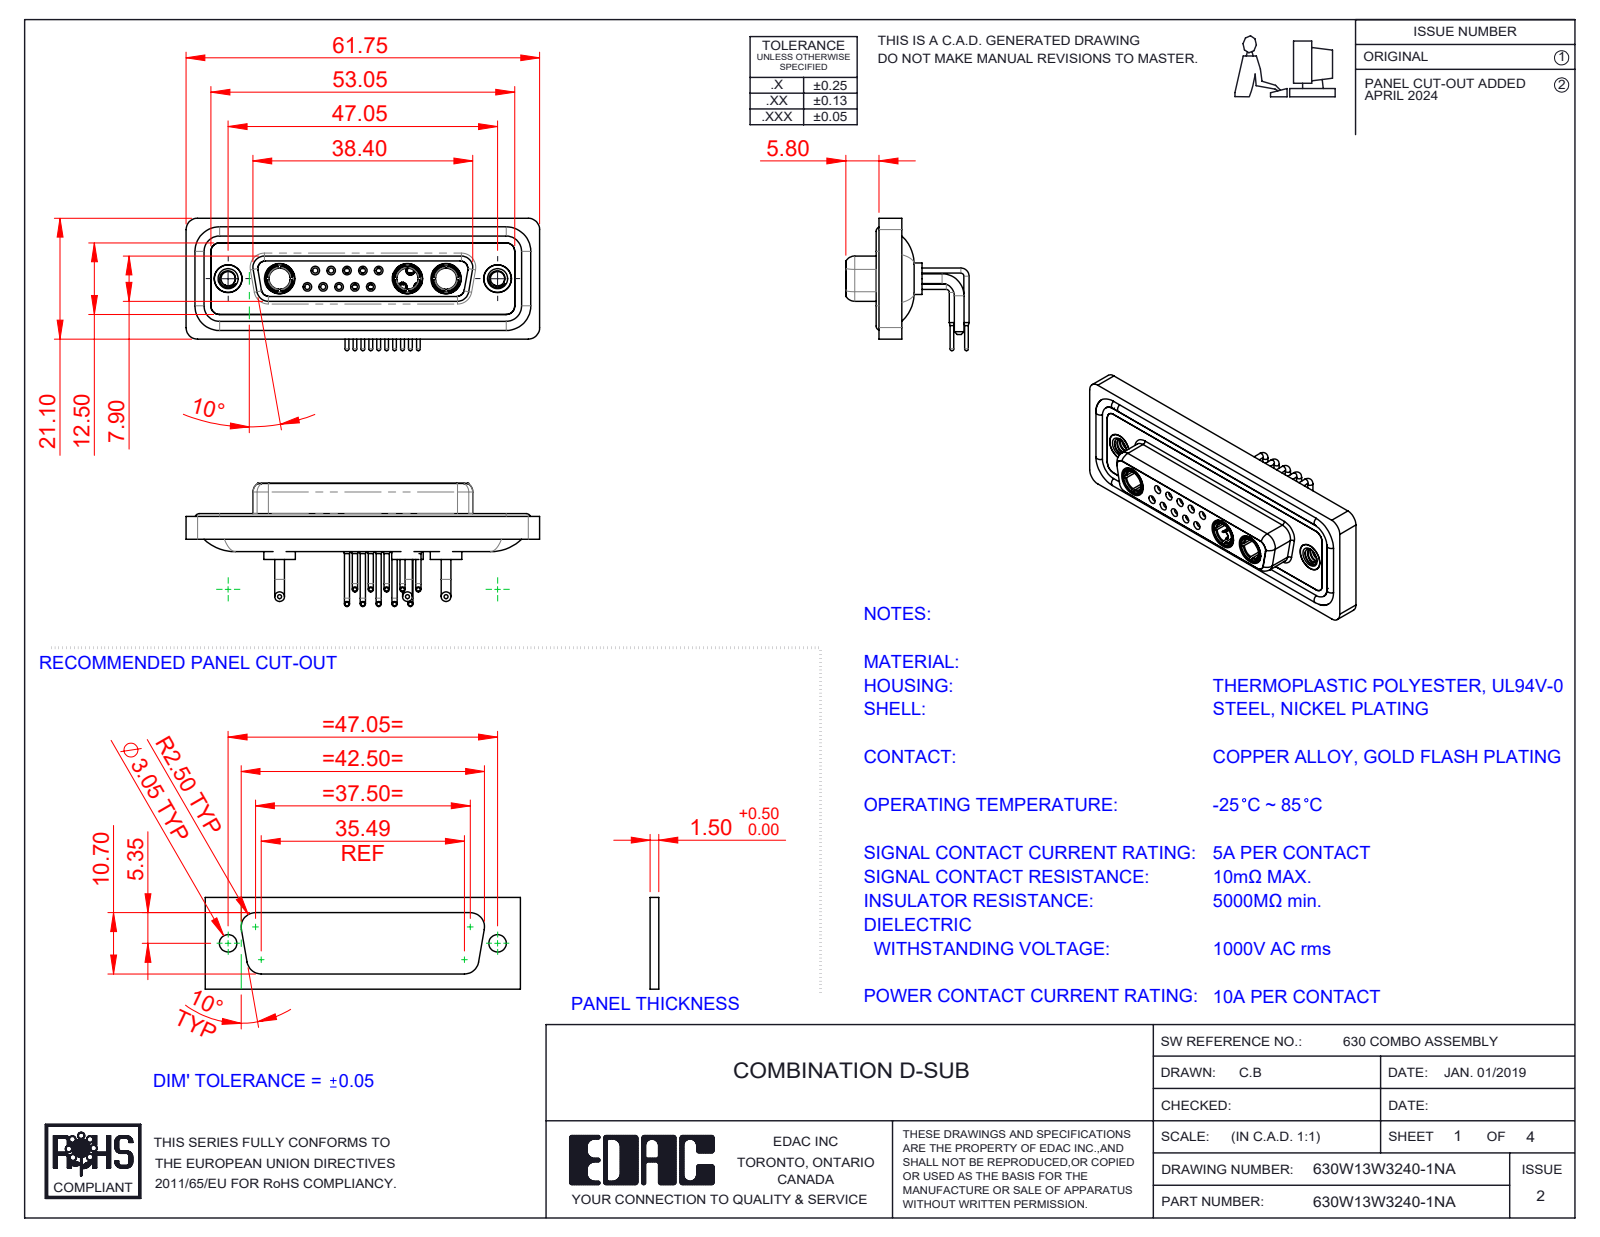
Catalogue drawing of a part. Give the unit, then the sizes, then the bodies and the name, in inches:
Units: inches
Overall size (bounding box): 2.431 × 0.91 × 0.848
Round holes (diameter × count): ⌀0.035 ×10, ⌀0.043 ×10, ⌀0.059 ×10, ⌀0.079 ×10, ⌀0.063 ×5, ⌀0.067 ×5, ⌀0.191 ×5, ⌀0.146 ×3, ⌀0.209 ×3, ⌀0.098 ×2, ⌀0.157 ×2, ⌀0.159 ×2
Round bosses / shafts (diameter × count): ⌀0.035 ×15, ⌀0.063 ×12, ⌀0.026 ×10, ⌀0.067 ×6, ⌀0.079 ×5, ⌀0.059 ×5, ⌀0.217 ×3, ⌀0.205 ×3
Partial cylindrical surfaces — rounded edges, fillets, slot ends (radius × count): R0.059 ×18, R0.079 ×18, R0.053 ×8, R0.063 ×8, R0.01 ×4, R0.02 ×4, R0.024 ×4, R0.026 ×4
Main face-to-face distances: 0.016, 0.071, 0.161, 0.043, 0.063, 0.059, 0.122, 0.098, 0.146, 0.055
Hole centre spacings: 0.124, 0.109, 0.218, 0.198, 0.327, 0.198, 0.295, 0.436
Volume: 0.506 in³ · Surface area: 21.93 in²
Bodies: 23 solids, 1144 faces (342 planar, 491 cylindrical, 311 other)
Part name (STEP PRODUCT): 630Combo Shell Rear_25 Contacts; 630W13W3240-1NA; 630Combo Contact Row 1_50 Contacts; 630Combo Contact Row 2_50 Contacts (+5 more)
STEP written by: SolidWorks 2023 (CONFIG_CONTROL_DESIGN)
